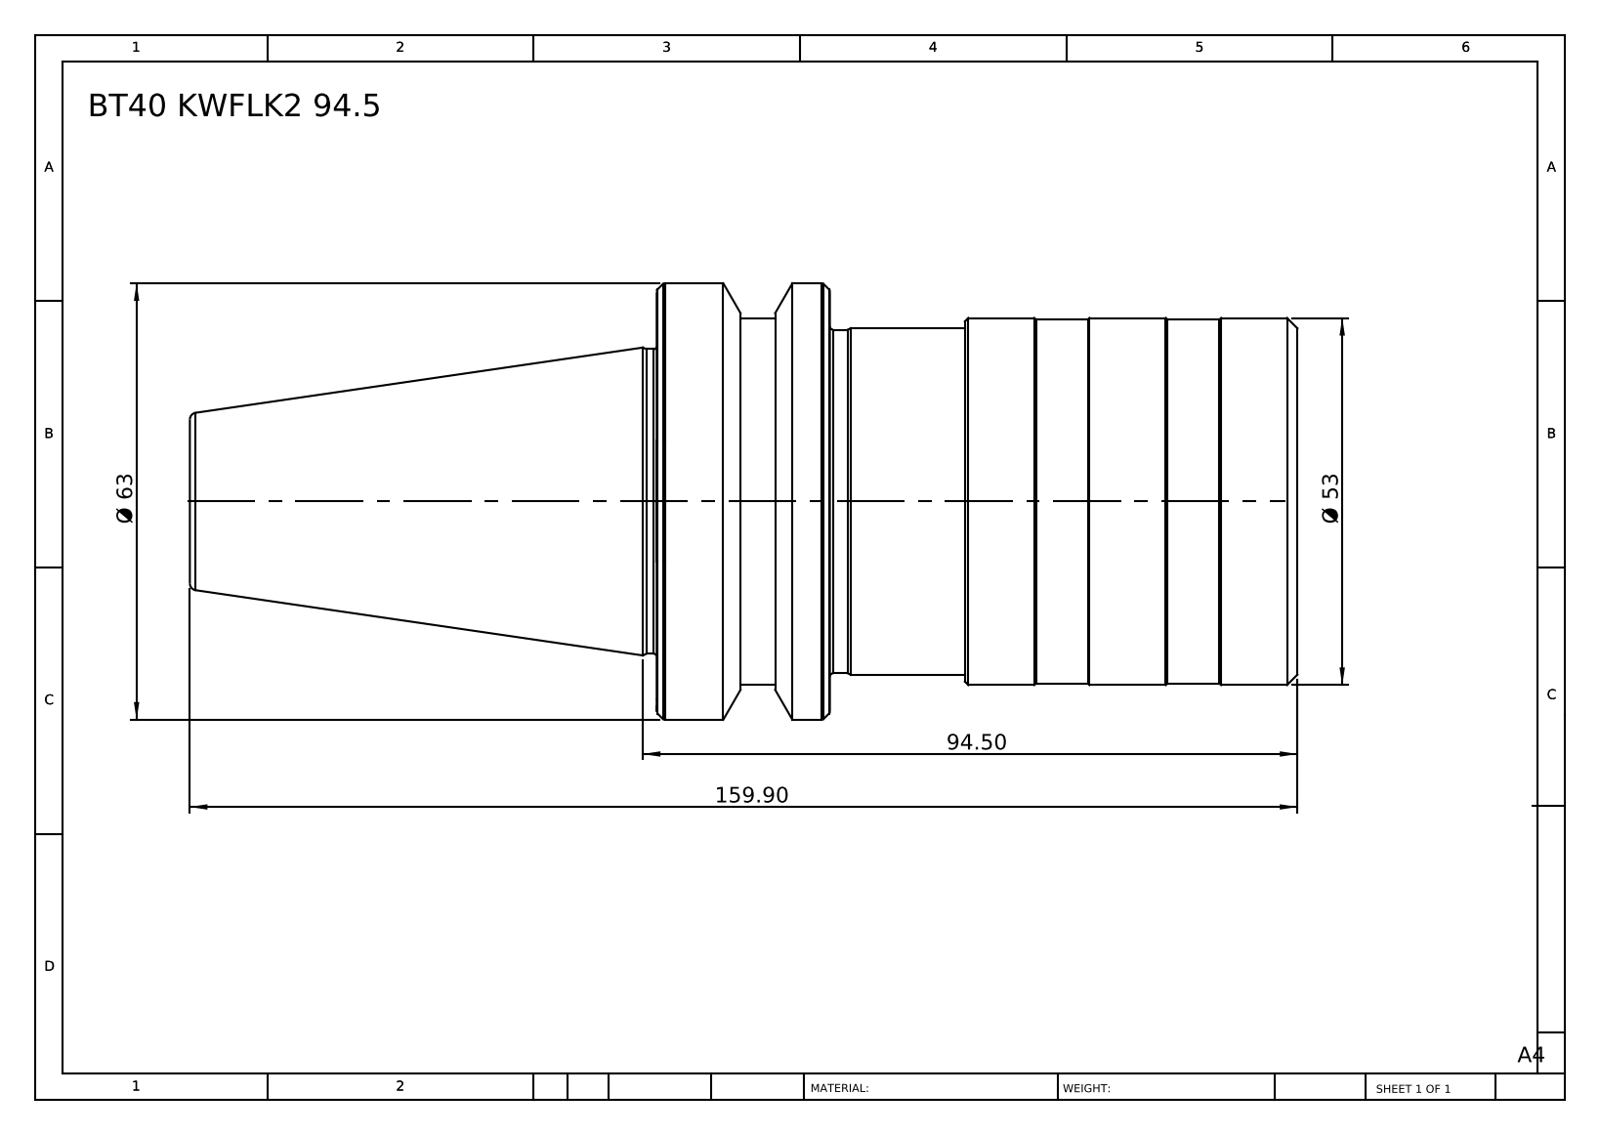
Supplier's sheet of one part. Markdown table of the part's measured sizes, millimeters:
| quantity | value |
| --- | --- |
| part name | BT40 KWFLK2 94.5 |
| STEP written by | SolidWorks 2014 (CONFIG_CONTROL_DESIGN) |
| units | millimeters |
| bodies | 1 solid, 75 faces (7 planar, 22 cylindrical, 46 other) |
| overall size | 159.9 × 63 × 63 |
| volume | 281 627 mm³ |
| surface area | 29 719 mm² |
| round bosses / shafts (diameter × count) | 63 × 1, 53 × 1, 52.5 × 1, 50 × 1, 49.6 × 1, 44 × 1 |
| main face-to-face distances | 92.5, 67.5, 25, 159.9, 92.4, 67.4, 48, 19.5, 44.5, 111.9 |
